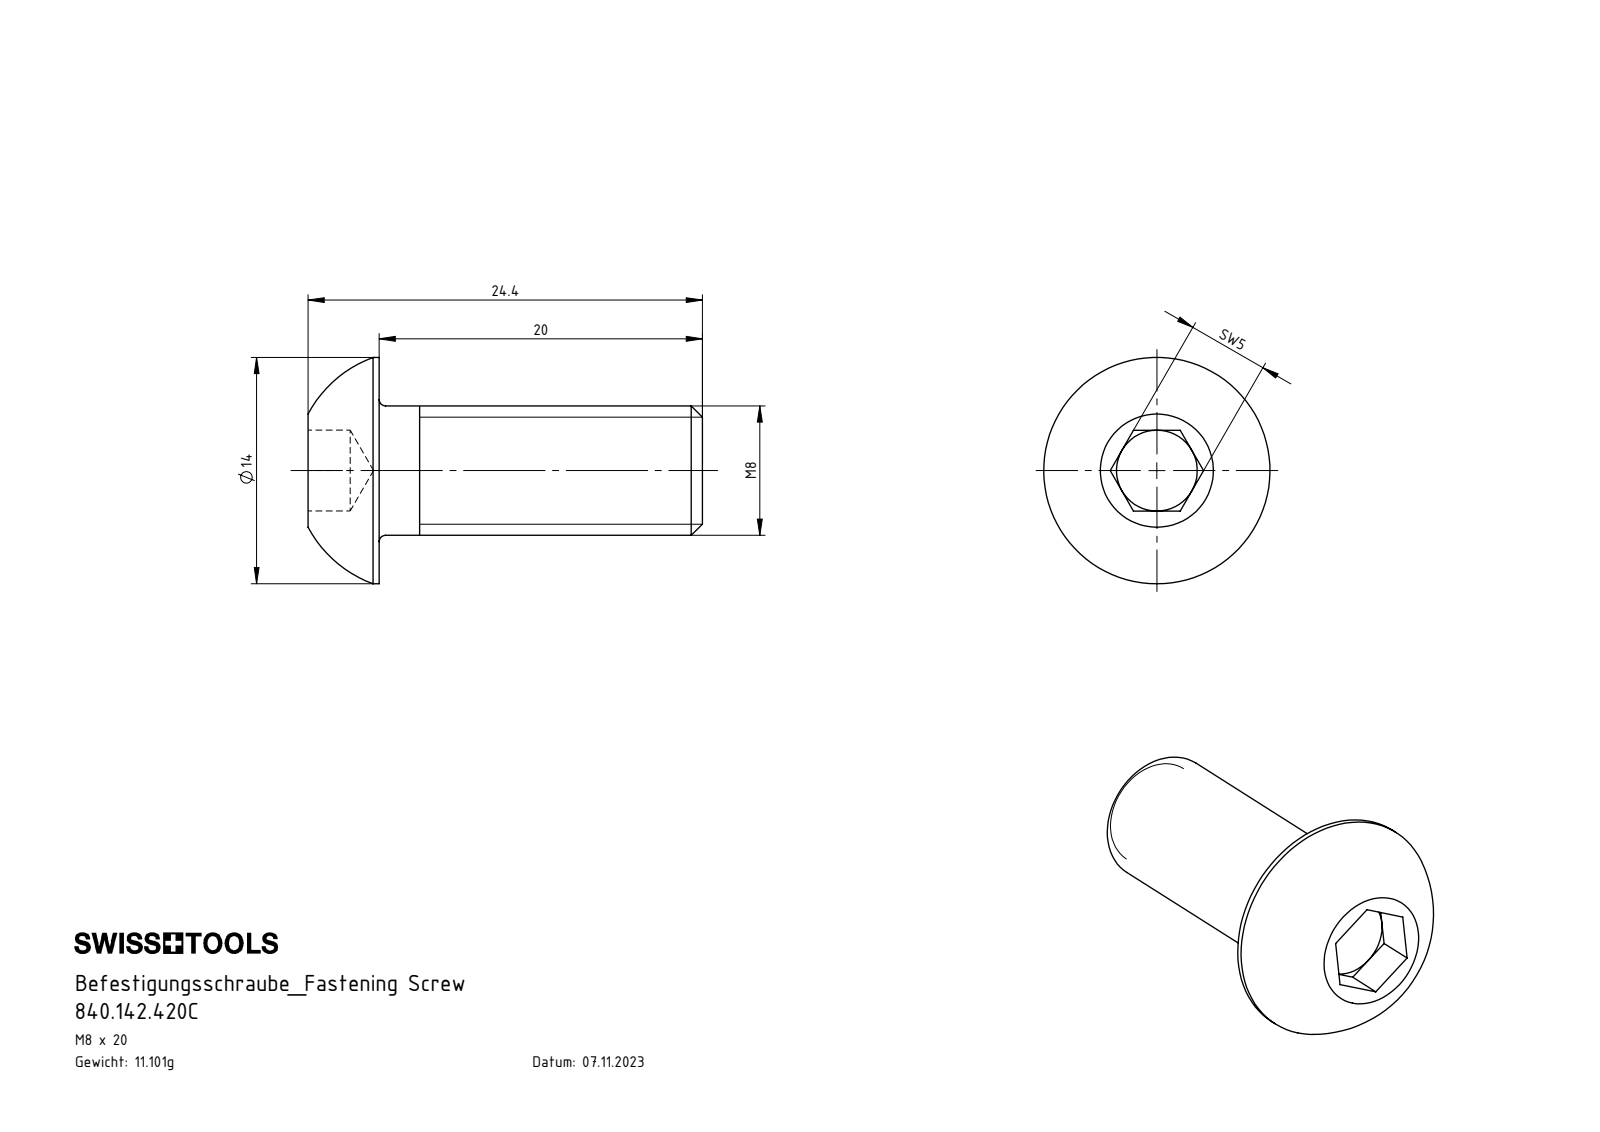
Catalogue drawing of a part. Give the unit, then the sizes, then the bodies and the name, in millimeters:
Units: millimetres
Overall size (bounding box): 24.4 × 14 × 14
Round bosses / shafts (diameter × count): ⌀14 ×1, ⌀8 ×1
Main face-to-face distances: 20, 5, 4.4, 24.4, 2.6, 1.8, 21.8
Volume: 1 414 mm³ · Surface area: 933 mm²
Bodies: 1 solid, 27 faces (15 planar, 4 cylindrical, 8 other)
Part name (STEP PRODUCT): 840.142.420C
STEP written by: SolidWorks 2022 (AUTOMOTIVE_DESIGN)
